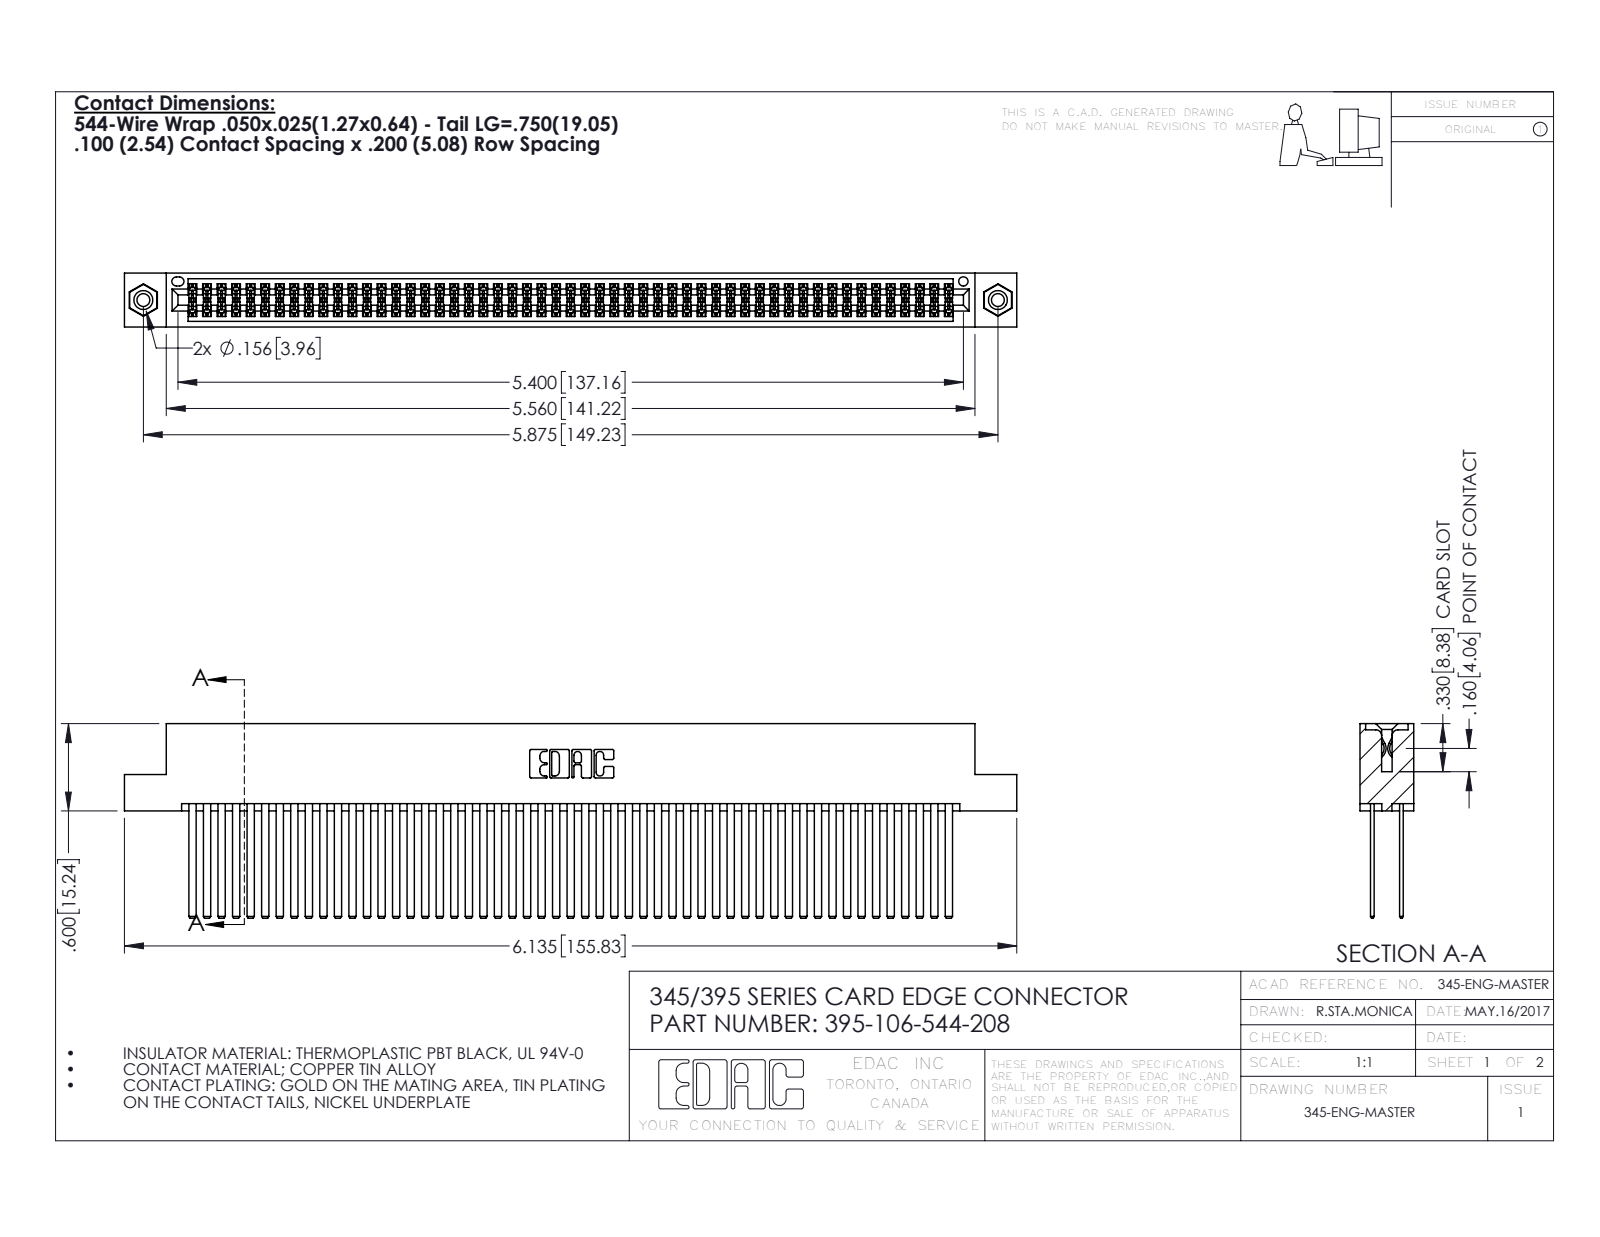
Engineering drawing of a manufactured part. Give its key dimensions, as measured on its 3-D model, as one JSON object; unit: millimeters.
{"part_name": "345-250-001_345-250-003-102; 395-106-544-208; 345-292-001_345-293-144; 345 Part_Flush Mounting Lugs - 0.156 Dia-TI", "step_written_by": "SolidWorks 2016 (CONFIG_CONTROL_DESIGN)", "units": "millimeters", "bodies": {"solids": 109, "faces": 4850, "planar": 3186, "cylindrical": 1648, "other": 16}, "overall_size": [155.8, 34, 9.4], "volume_mm3": 16710, "surface_area_mm2": 29300, "round_holes": [[2.3, 2], [3.2, 2], [4, 2], [1.6, 1]], "round_bosses_or_shafts": [[3.9, 2]], "partial_cylinders_radius": [[0.2, 159], [0.3, 22], [0.2, 6], [0.8, 6], [0.7, 3], [0.4, 2], [0.5, 2], [0.6, 2]], "face_to_face_distances": [5.1, 0.6, 1.8, 2.5, 6.9, 7.6, 5.7, 4.4, 9.4, 1.3], "hole_center_spacings": [6.9, 143.2, 149.2]}
